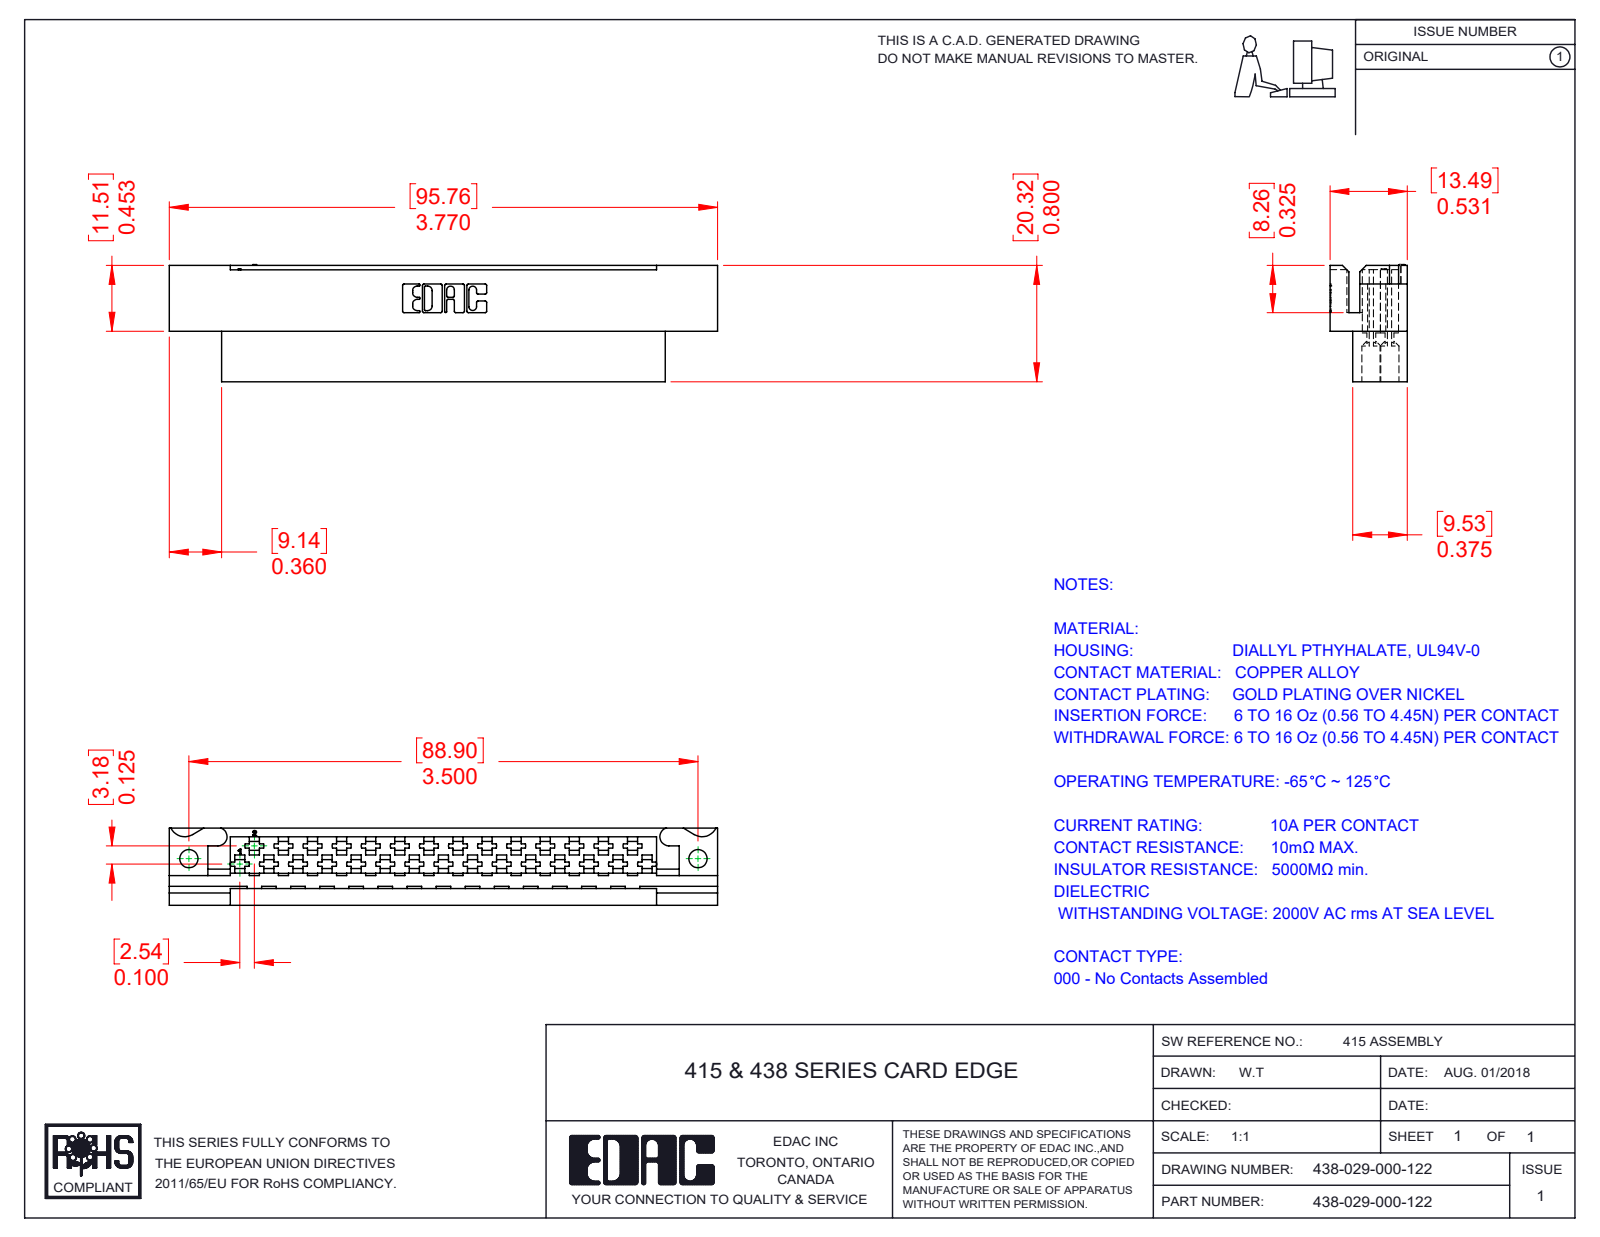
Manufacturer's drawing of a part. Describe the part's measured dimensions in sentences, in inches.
The part is named "438-029-000-122; 438-210-001_438-210-029-112". Its 3-D file was written by "SolidWorks 2016 (CONFIG_CONTROL_DESIGN)". It is 1 solid with 910 faces: 693 planar, 108 cylindrical and 109 other. Overall it measures 3.77 by 0.805 by 0.531 inches. Its volume is 0.886 cubic inches and its surface area 22.11 square inches. Round holes: 29 of diameter 0.13, 1 of diameter 0.125, 1 of diameter 0.125. Partial cylindrical surfaces (rounded edges, fillets, slot ends): 22 of radius 0.01, 6 of radius 0.007, 6 of radius 0.031, 3 of radius 0.026, 2 of radius 0.063, 2 of radius 0.106. The main face-to-face distances are 0.531, 0.375, 0.156, 0.125, 0.048, 0.125, 0.172, 0.047, 0.202, 0.029. The hole center spacings are 0.16, 0.2, 0.325, 0.4, 0.515, 0.6, 0.711, 0.8.
